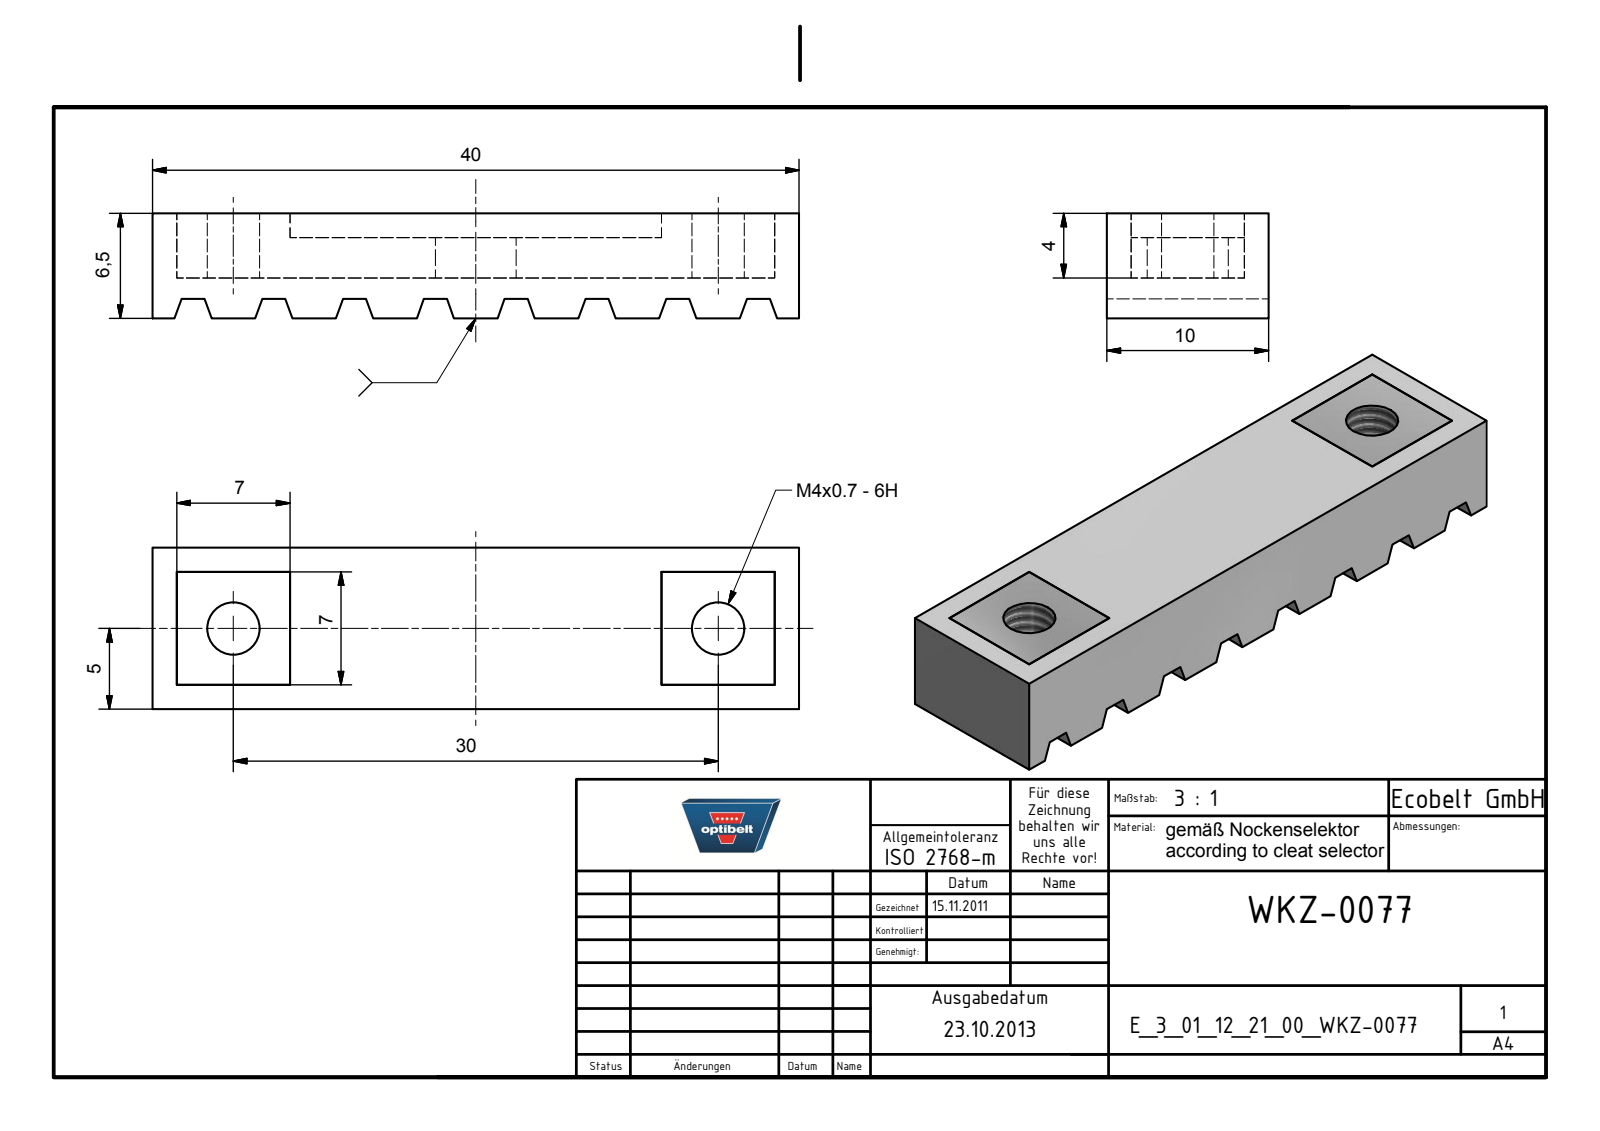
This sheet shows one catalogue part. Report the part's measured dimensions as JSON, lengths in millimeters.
{"part_name": "E_3_01_12_21_00_WKZ-0077; E_3_01_12_21_00_WKZ-0077-Teil1; E_3_01_12_21_00_WKZ-0077-Teil2", "step_written_by": "Autodesk Inventor 2025 (AUTOMOTIVE_DESIGN)", "units": "millimeters", "bodies": {"solids": 2, "faces": 59, "planar": 56, "cylindrical": 3, "other": 0}, "overall_size": [40, 10, 6.5], "volume_mm3": 2306, "surface_area_mm2": 3045, "round_holes": [[3.24, 2], [5, 1]], "face_to_face_distances": [1.5, 2.5, 8.5, 4, 7, 10, 5, 6.5, 4.7, 9.4], "hole_center_spacings": [15, 30]}
